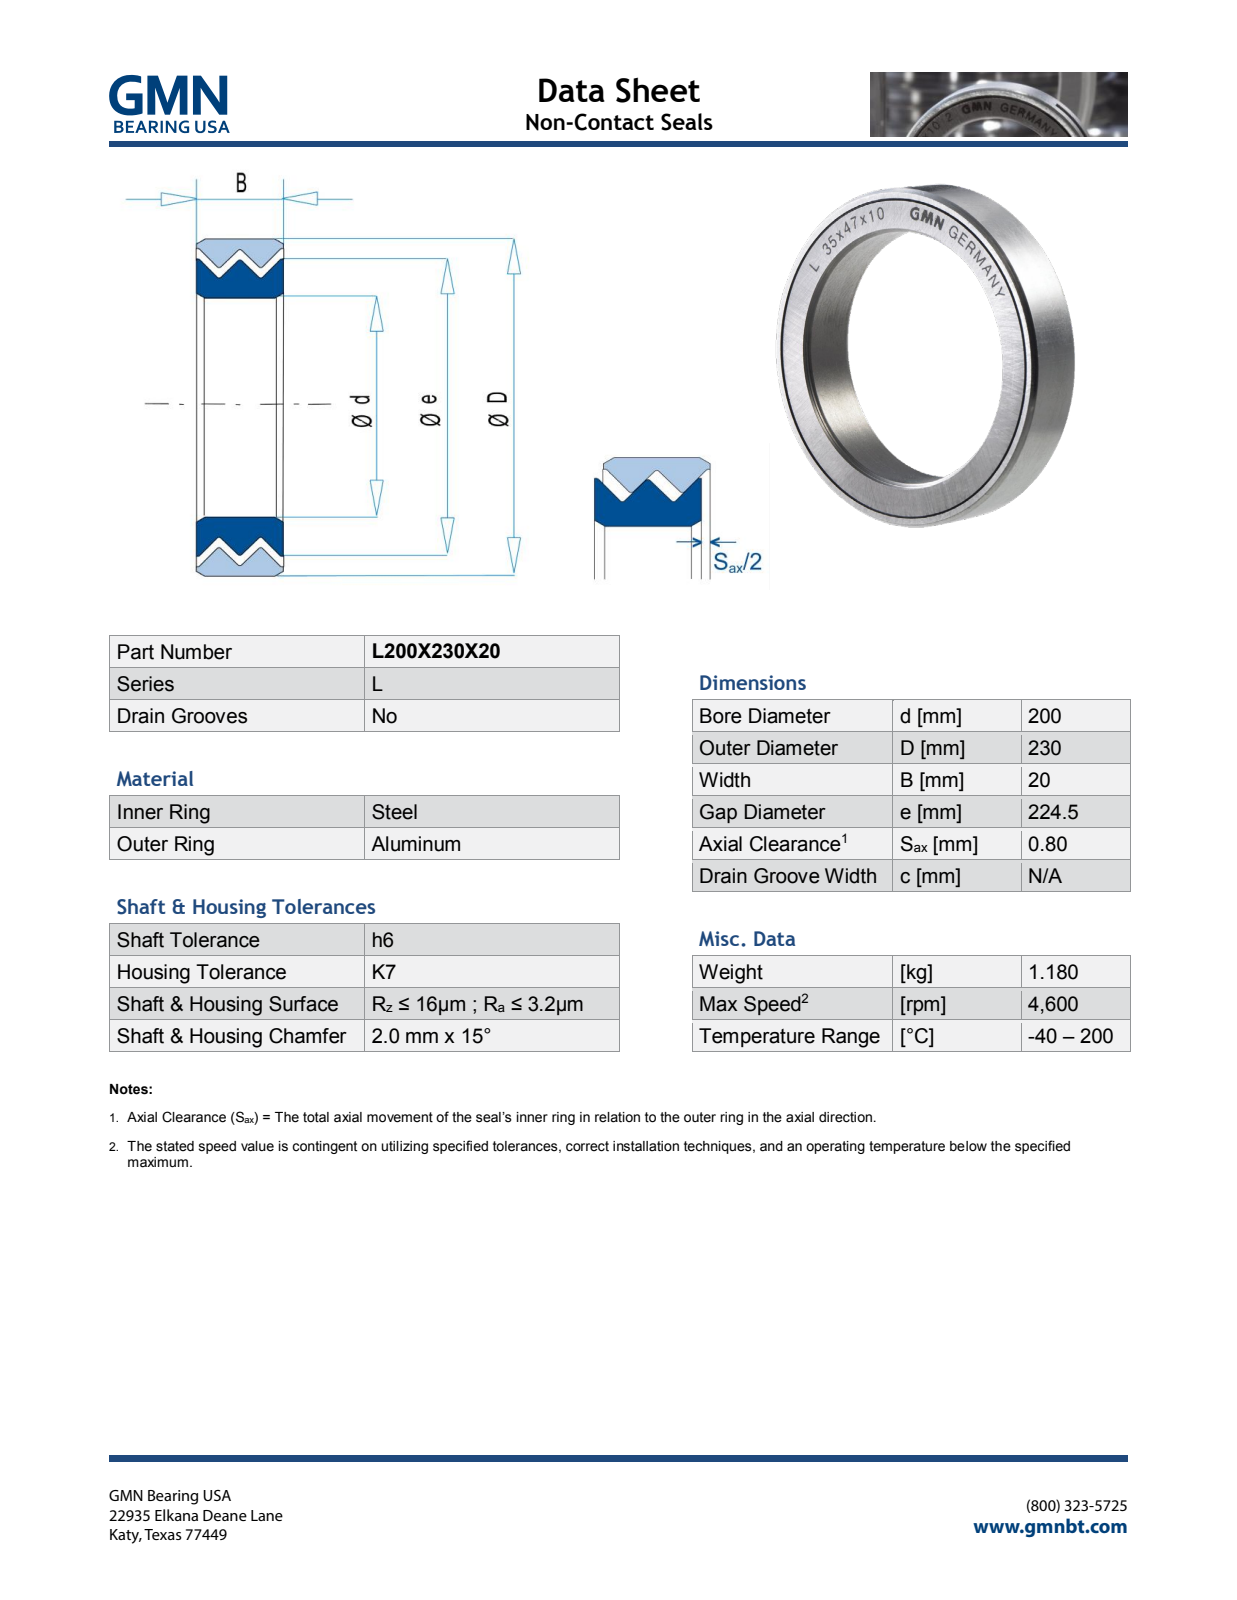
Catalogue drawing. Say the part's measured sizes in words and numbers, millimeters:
The part is named "L200X230X20_PRT". Its 3-D file was written by "PRO/ENGINEER BY PARAMETRIC TECHNOLOGY CORPORATION, 2013150 (AUTOMOTIVE_DESIGN)". It is 1 solid with 718 faces: 638 planar, 8 cylindrical and 72 other. Overall it measures 230 by 230 by 20.08 millimeters. Its volume is 194 087 cubic millimeters and its surface area 81 244 square millimeters. Round holes: 1 of diameter 200, 1 of diameter 223.91. Round bosses or shafts: 1 of diameter 230. The main face-to-face distances are 20, 20.08, 1.14, 9.1, 1.16, 7.96, 6.82, 9.09, 6.44, 0.96.
